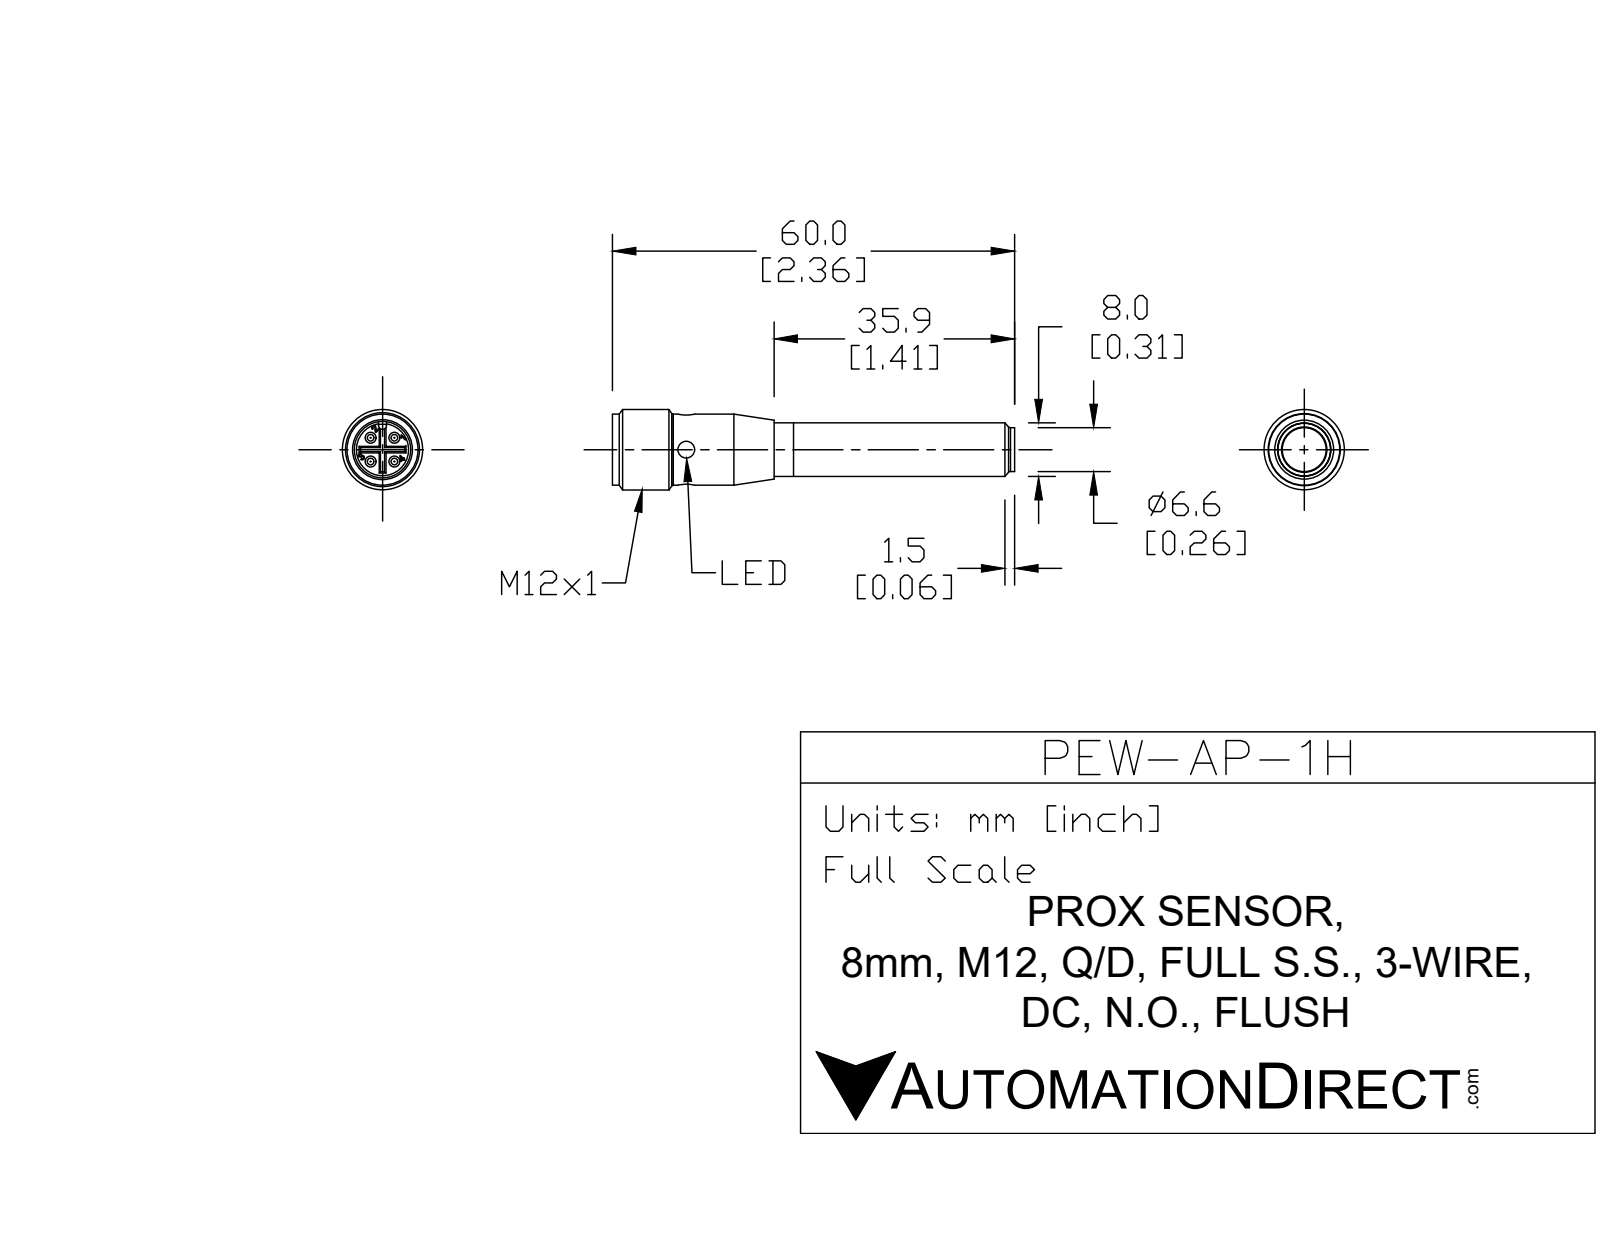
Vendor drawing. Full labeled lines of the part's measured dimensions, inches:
Part name (STEP PRODUCT): PEW-AP-1H
STEP written by: SolidWorks 2017 (AUTOMOTIVE_DESIGN)
Units: inches
Bodies: 3 solids, 103 faces (27 planar, 27 cylindrical, 49 other)
Overall size (bounding box): 2.362 × 0.591 × 0.512
Volume: 0.267 in³ · Surface area: 4.763 in²
Round holes (diameter × count): ⌀0.098 ×2, ⌀0.272 ×1, ⌀0.331 ×1
Round bosses / shafts (diameter × count): ⌀0.472 ×1, ⌀0.417 ×1, ⌀0.315 ×1, ⌀0.311 ×1, ⌀0.258 ×1
Partial cylindrical surfaces — rounded edges, fillets, slot ends (radius × count): R0.024 ×1
Main face-to-face distances: 0.512, 0.157, 0.315, 1.382, 1.224, 1.539, 2.012, 0.787, 0.63, 0.472
